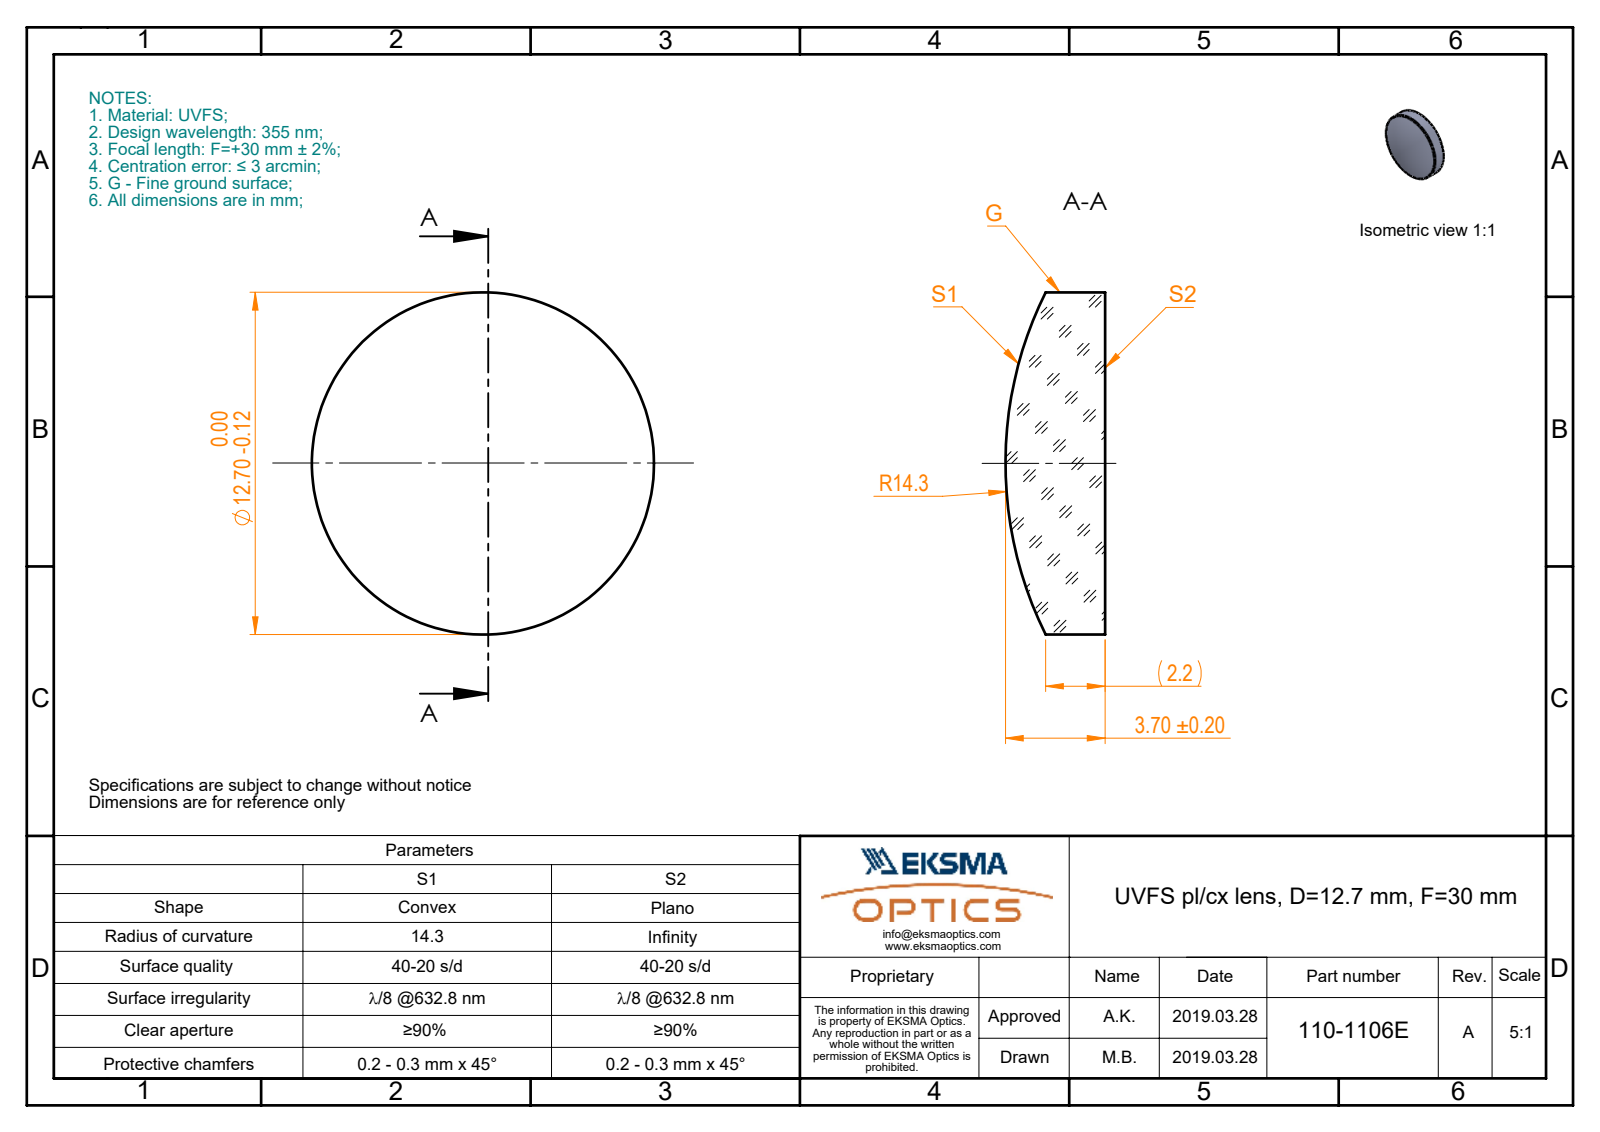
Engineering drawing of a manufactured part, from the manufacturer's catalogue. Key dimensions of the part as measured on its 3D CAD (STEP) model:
Part name (STEP PRODUCT): 110-1106E UVFS pl-cx 12.7 F30
STEP written by: SolidWorks 2017 (CONFIG_CONTROL_DESIGN)
Units: millimetres
Bodies: 1 solid, 5 faces (1 planar, 2 cylindrical, 2 other)
Overall size (bounding box): 12.7 × 12.7 × 3.7
Volume: 376 mm³ · Surface area: 349 mm²
Round bosses / shafts (diameter × count): ⌀12.7 ×1
